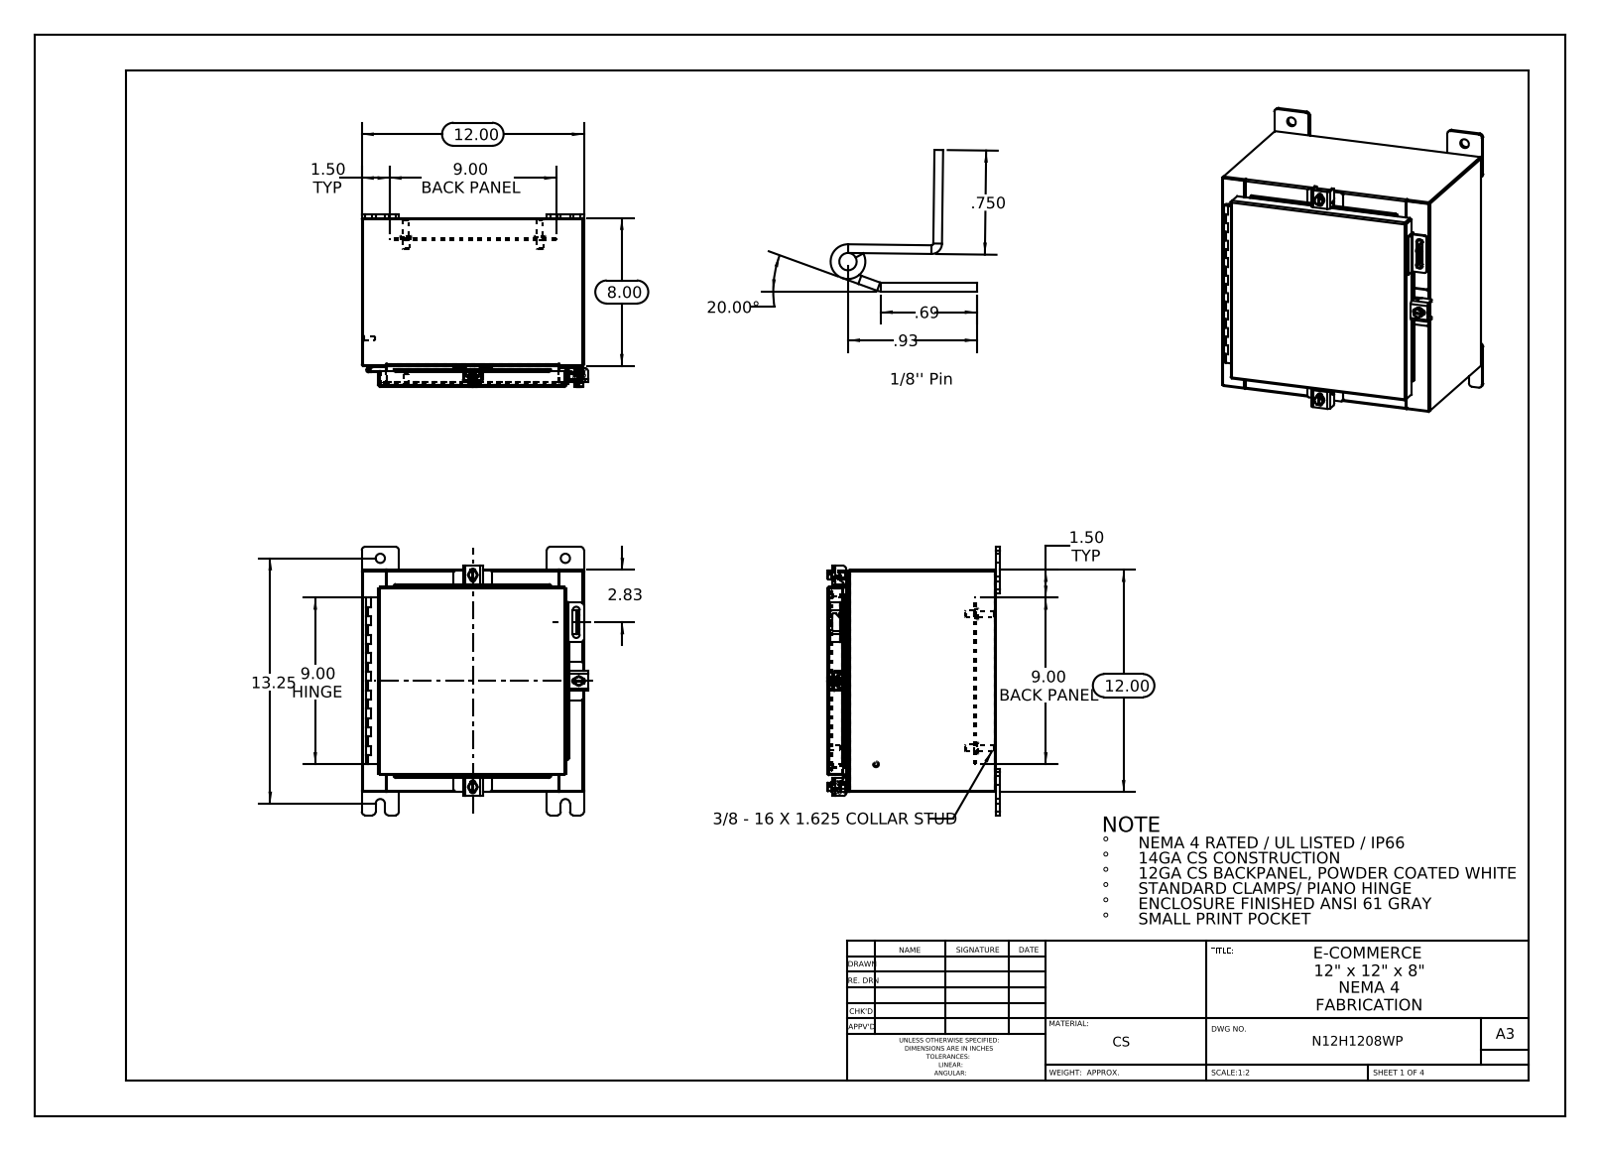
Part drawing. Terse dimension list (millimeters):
name: N12H1208WP Standard Clamps; N12H1208WP; N12H1208WP Clamp Assembly; Clamp Top_RTP31 (+8 more)
written by: SolidWorks 2014 (CONFIG_CONTROL_DESIGN)
unit: mm
bodies: 34 solids, 1080 faces (578 planar, 418 cylindrical, 84 other)
size: 368.3 × 310.2 × 236.6
volume: 1 173 000 mm³; area: 1 182 000 mm²
holes: 8× ⌀12.7, 3× ⌀5.4, 3× ⌀6.6, 2× ⌀3.2, 1× ⌀3.2
bosses: 4× ⌀15.9, 4× ⌀9.5, 4× ⌀8.4, 4× ⌀6.4, 3× ⌀12.7, 3× ⌀10.1, 2× ⌀8, 2× ⌀6
rounds: 24× R4.8, 23× R0.3, 21× R2.2, 18× R1.5, 10× R3.2, 6× R0.5, 6× R2.5, 6× R3
face distances: 1.9, 302.9, 229.6, 301, 304.8, 201.3, 28.3, 227.7, 231.5, 25.4
hole spacings: 106.4, 254.7, 56.5, 83.8, 127.3, 129, 184.2, 184.2
